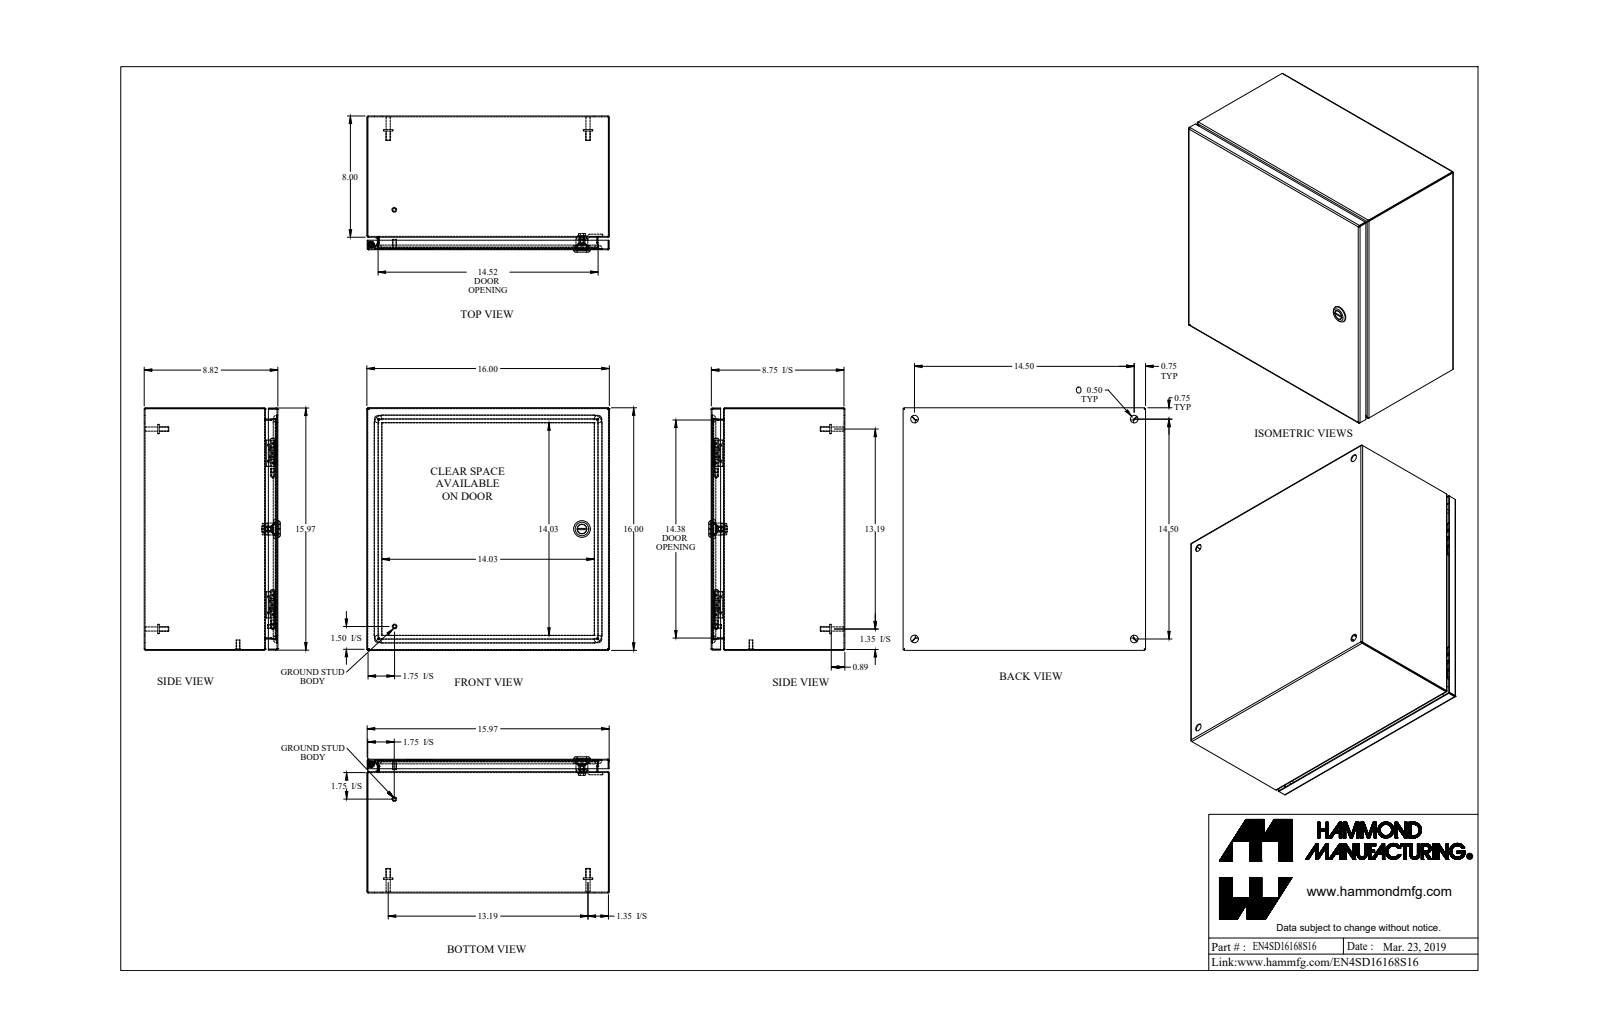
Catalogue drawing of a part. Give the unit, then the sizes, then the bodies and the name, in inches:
Units: inches
Overall size (bounding box): 16 × 16 × 8.981
Round holes (diameter × count): ⌀0.5 ×5, ⌀0.172 ×1, ⌀0.197 ×1, ⌀0.24 ×1, ⌀0.242 ×1, ⌀0.387 ×1, ⌀0.63 ×1, ⌀0.768 ×1
Round bosses / shafts (diameter × count): ⌀0.313 ×6, ⌀0.625 ×4, ⌀0.275 ×4, ⌀0.25 ×2, ⌀1.1 ×1, ⌀0.785 ×1, ⌀0.625 ×1, ⌀0.525 ×1
Partial cylindrical surfaces — rounded edges, fillets, slot ends (radius × count): R0.029 ×21, R0.086 ×21, R0.188 ×12, R0.006 ×4, R0.062 ×4, R0.25 ×4, R0.499 ×4, R0.125 ×2
Main face-to-face distances: 0.057, 15.943, 0.057, 15.886, 8.707, 8.764, 8.764, 8.821, 16, 7.943
Hole centre spacings: 14.5, 7.327, 15.272, 20.506
Volume: 71.92 in³ · Surface area: 2 443 in²
Bodies: 22 solids, 656 faces (303 planar, 211 cylindrical, 142 other)
Part name (STEP PRODUCT): EN4SD16168S16_Default
STEP written by: SolidWorks 2019 (CONFIG_CONTROL_DESIGN)
